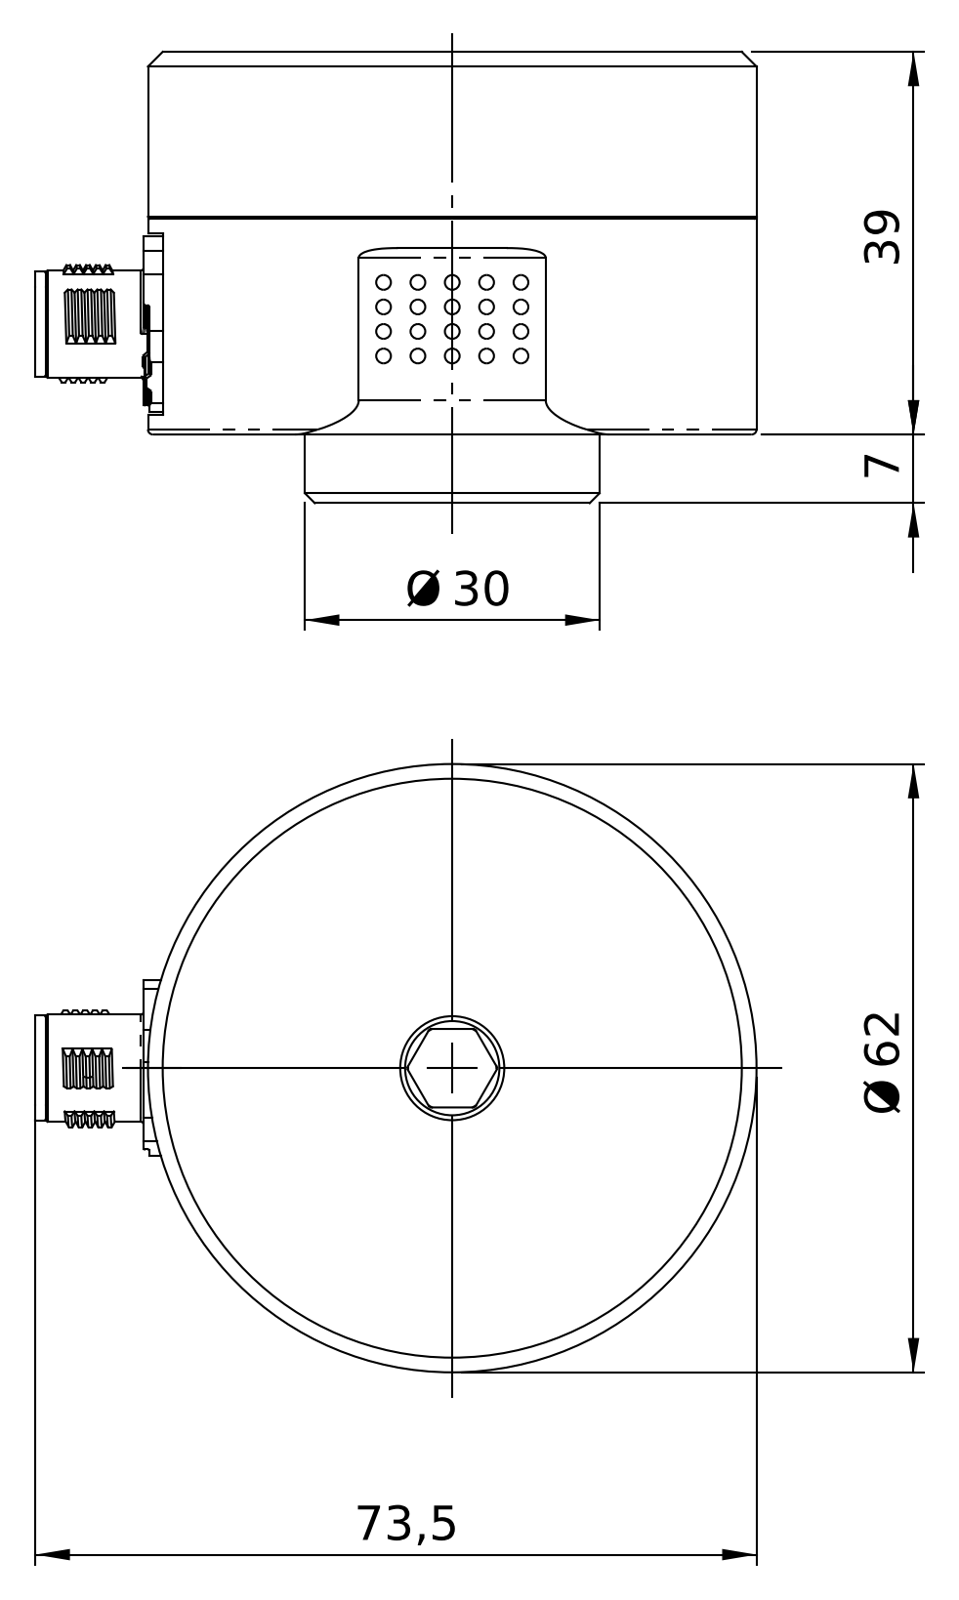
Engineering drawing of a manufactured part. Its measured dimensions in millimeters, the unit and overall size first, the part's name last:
Units: millimetres
Overall size (bounding box): 73.45 × 62 × 46
Round holes (diameter × count): ⌀8.3 ×1, ⌀9 ×1, ⌀9.6 ×1, ⌀14.9 ×1, ⌀15 ×1
Round bosses / shafts (diameter × count): ⌀0.8 ×8, ⌀62 ×1, ⌀30 ×1, ⌀10.9 ×1, ⌀10.7 ×1
Partial cylindrical surfaces — rounded edges, fillets, slot ends (radius × count): R0.2 ×10, R1 ×2, R3.5 ×2, R0.6 ×1, R6 ×1, R9 ×1
Main face-to-face distances: 39, 7, 46, 59, 8, 1, 17, 38, 29, 22
Volume: 116 965 mm³ · Surface area: 16 874 mm²
Bodies: 1 solid, 462 faces (292 planar, 43 cylindrical, 127 other)
Part name (STEP PRODUCT): 02.117.020
STEP written by: SolidWorks 2020 (AUTOMOTIVE_DESIGN)
